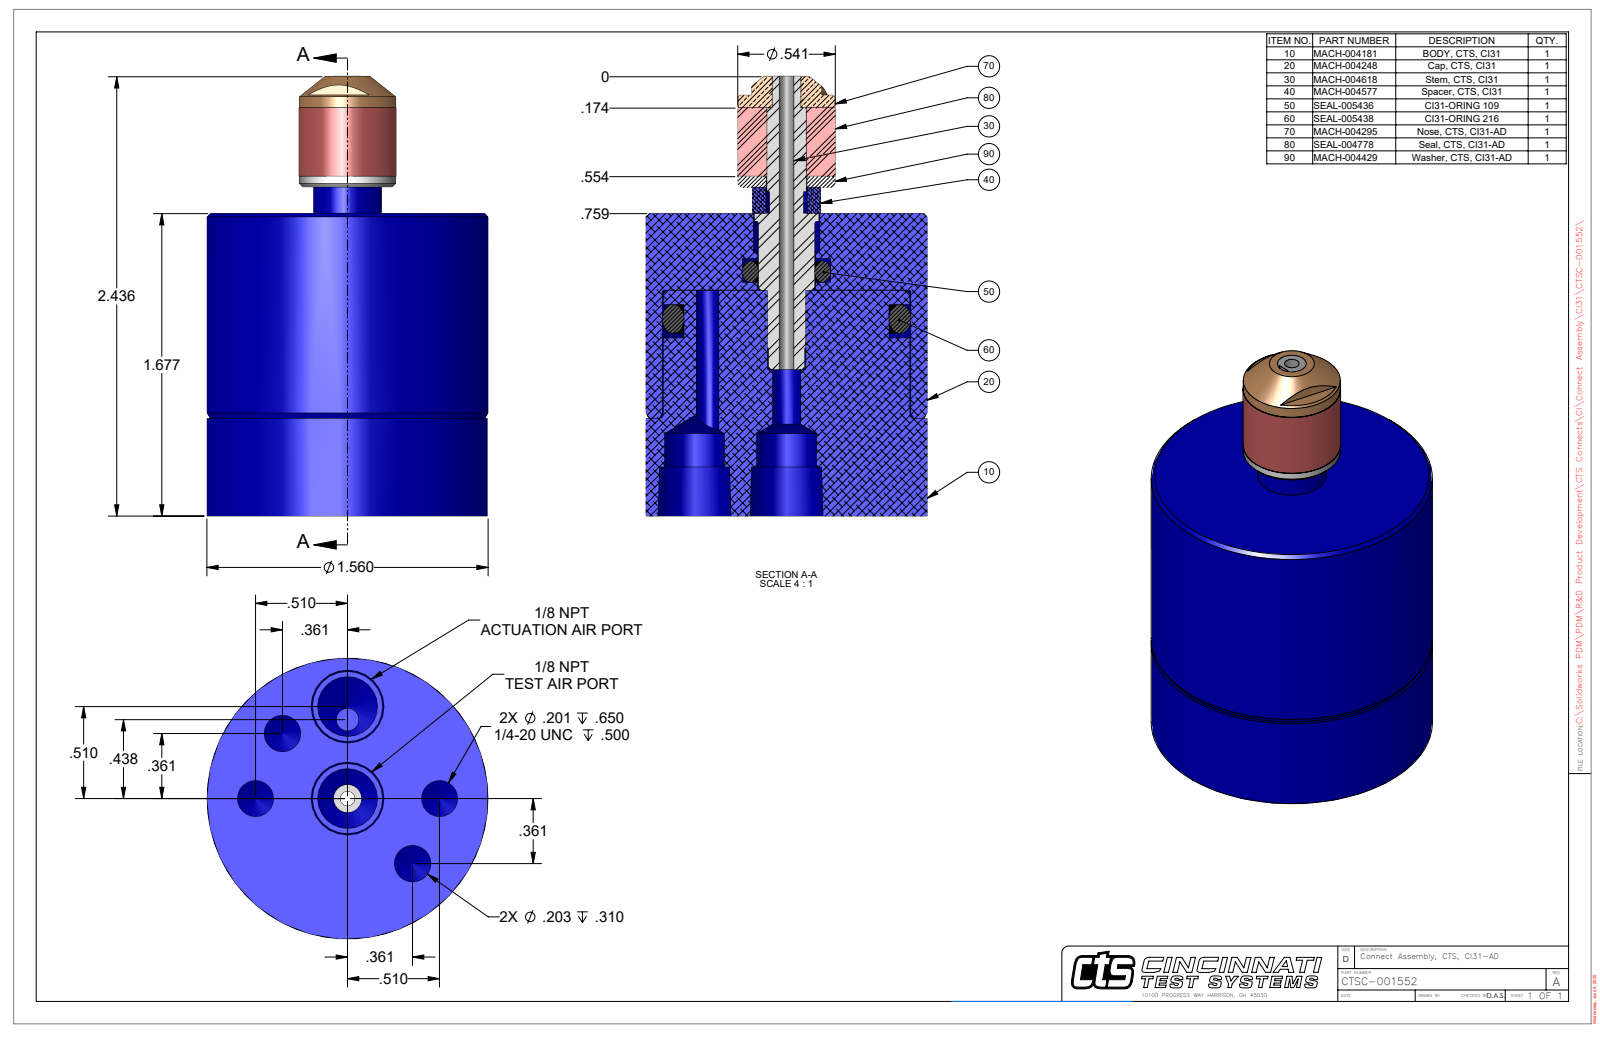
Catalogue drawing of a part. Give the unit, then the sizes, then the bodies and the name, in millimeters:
Units: millimetres
Overall size (bounding box): 61.9 × 39.6 × 39.6
Round holes (diameter × count): ⌀5.1 ×2, ⌀5.2 ×2, ⌀8.4 ×2, ⌀2.1 ×1, ⌀3.2 ×1, ⌀4 ×1, ⌀9.3 ×1, ⌀35 ×1
Round bosses / shafts (diameter × count): ⌀39.6 ×1, ⌀34.7 ×1, ⌀13.7 ×1, ⌀13.7 ×1, ⌀9.6 ×1, ⌀9.1 ×1
Main face-to-face distances: 42.6, 13.8, 28.8, 46.3, 32.5, 3.7, 20.6, 6.9, 22, 25.7
Hole centre spacings: 13, 9.9, 23.9, 17.1, 18.3, 1.8, 9.4, 11.1
Volume: 51 670 mm³ · Surface area: 12 150 mm²
Bodies: 1 solid, 91 faces (23 planar, 38 cylindrical, 30 other)
Part name (STEP PRODUCT): CTSC-001552
STEP written by: SolidWorks 2023 (AUTOMOTIVE_DESIGN)
